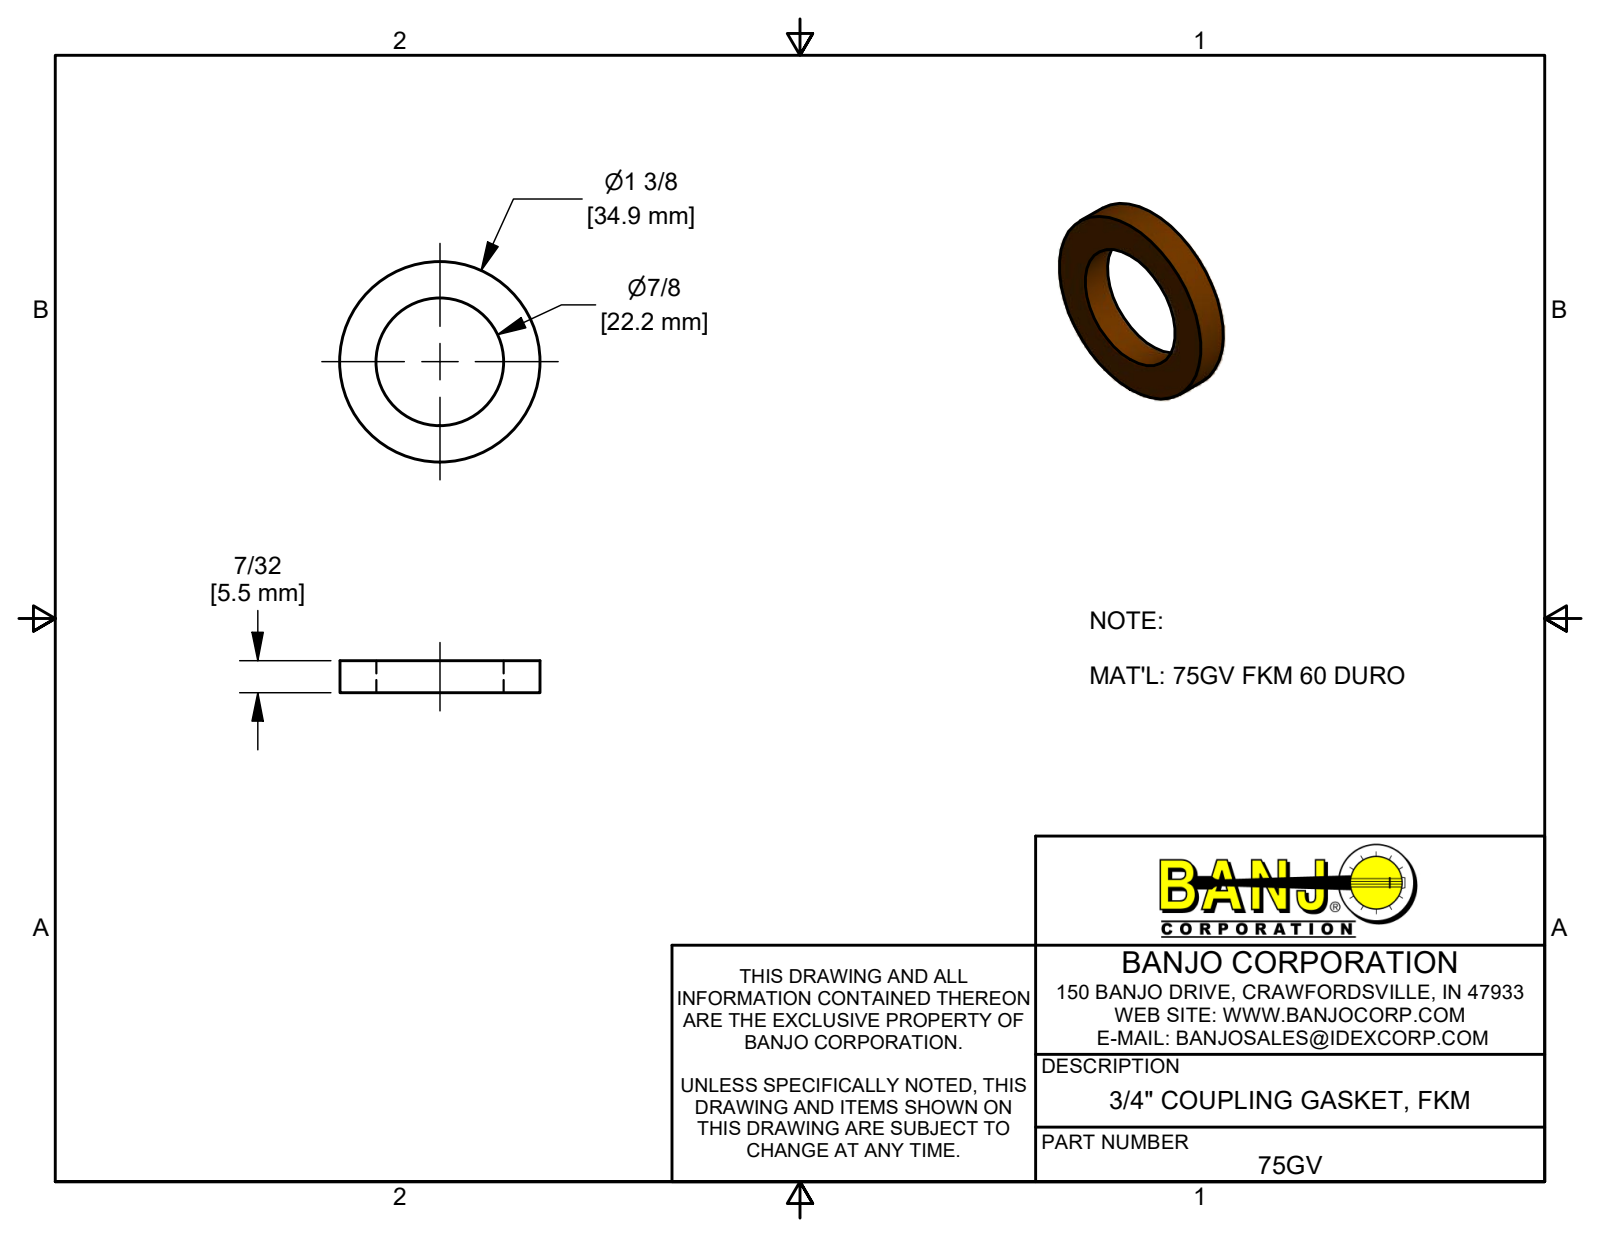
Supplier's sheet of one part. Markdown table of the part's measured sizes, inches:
| quantity | value |
| --- | --- |
| part name | 75GV |
| STEP written by | Autodesk Inventor 2019 (AUTOMOTIVE_DESIGN) |
| units | inches |
| bodies | 1 solid, 4 faces (2 planar, 2 cylindrical, 0 other) |
| overall size | 1.375 × 1.375 × 0.218 |
| volume | 0.193 in³ |
| surface area | 3.308 in² |
| round holes (diameter × count) | 0.875 × 1 |
| round bosses / shafts (diameter × count) | 1.375 × 1 |
| main face-to-face distances | 0.218 |
